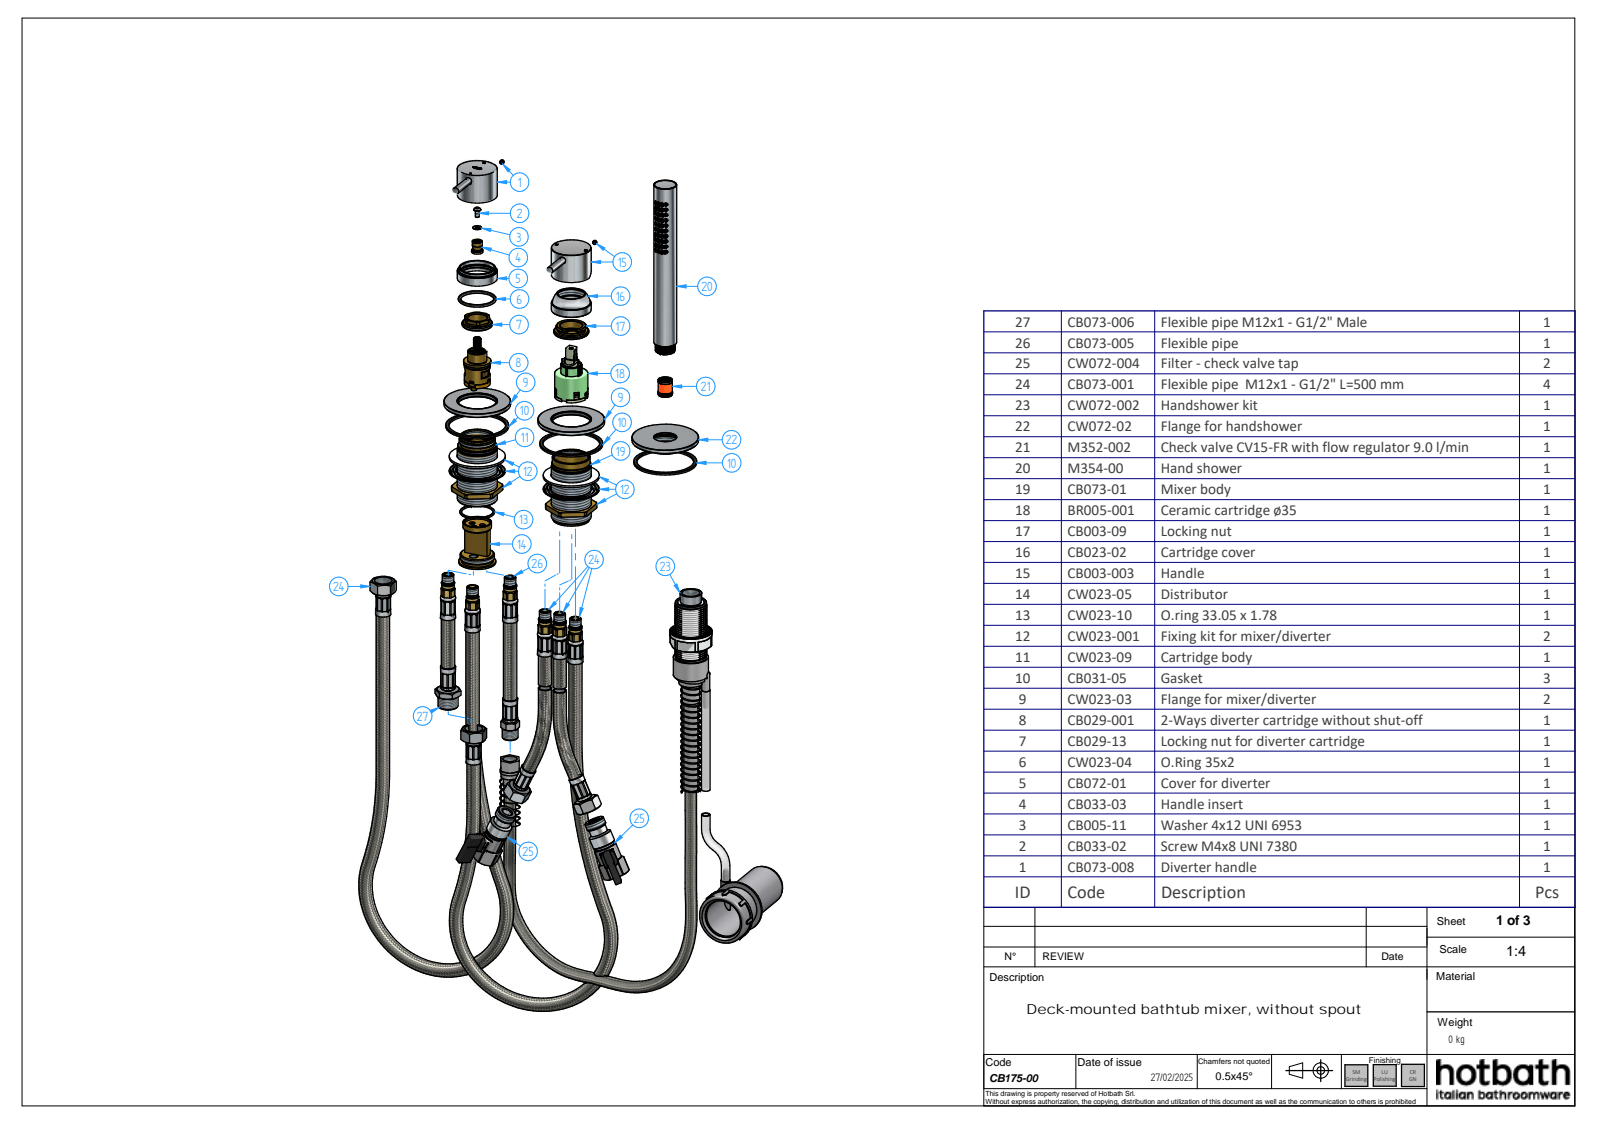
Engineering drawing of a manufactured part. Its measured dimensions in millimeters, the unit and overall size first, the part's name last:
Units: millimetres
Overall size (bounding box): 290 × 192.35 × 86.5
Round holes (diameter × count): ⌀3.2 ×40, ⌀5 ×4, ⌀67 ×3, ⌀3.3 ×2, ⌀7.2 ×2, ⌀39 ×2, ⌀39.92 ×2, ⌀42.3 ×2, ⌀10 ×1, ⌀10.5 ×1, ⌀11 ×1, ⌀12.9 ×1
Round bosses / shafts (diameter × count): ⌀70 ×3, ⌀57 ×3, ⌀43 ×2, ⌀42 ×2, ⌀7 ×2, ⌀28 ×1, ⌀21.17 ×1, ⌀17 ×1
Partial cylindrical surfaces — rounded edges, fillets, slot ends (radius × count): R0.35 ×4, R5 ×4, R0.59 ×3, R0.77 ×3, R0.22 ×2, R0.23 ×2, R0.28 ×2, R0.42 ×2
Main face-to-face distances: 4, 0.5, 3.5, 1.7, 2.3, 1.2, 42.6, 42.1, 40.9, 38.6
Hole centre spacings: 7.21, 12.65, 6, 12, 18.44, 4, 18, 24.33
Volume: 79 437 mm³ · Surface area: 93 442 mm²
Bodies: 13 solids, 1002 faces (294 planar, 261 cylindrical, 447 other)
Part name (STEP PRODUCT): CB175-00; CW023-03_oa_0; CW023-03_oa_1; CB003-003_oa_2 (+8 more)
STEP written by: Solid Edge (AUTOMOTIVE_DESIGN)
